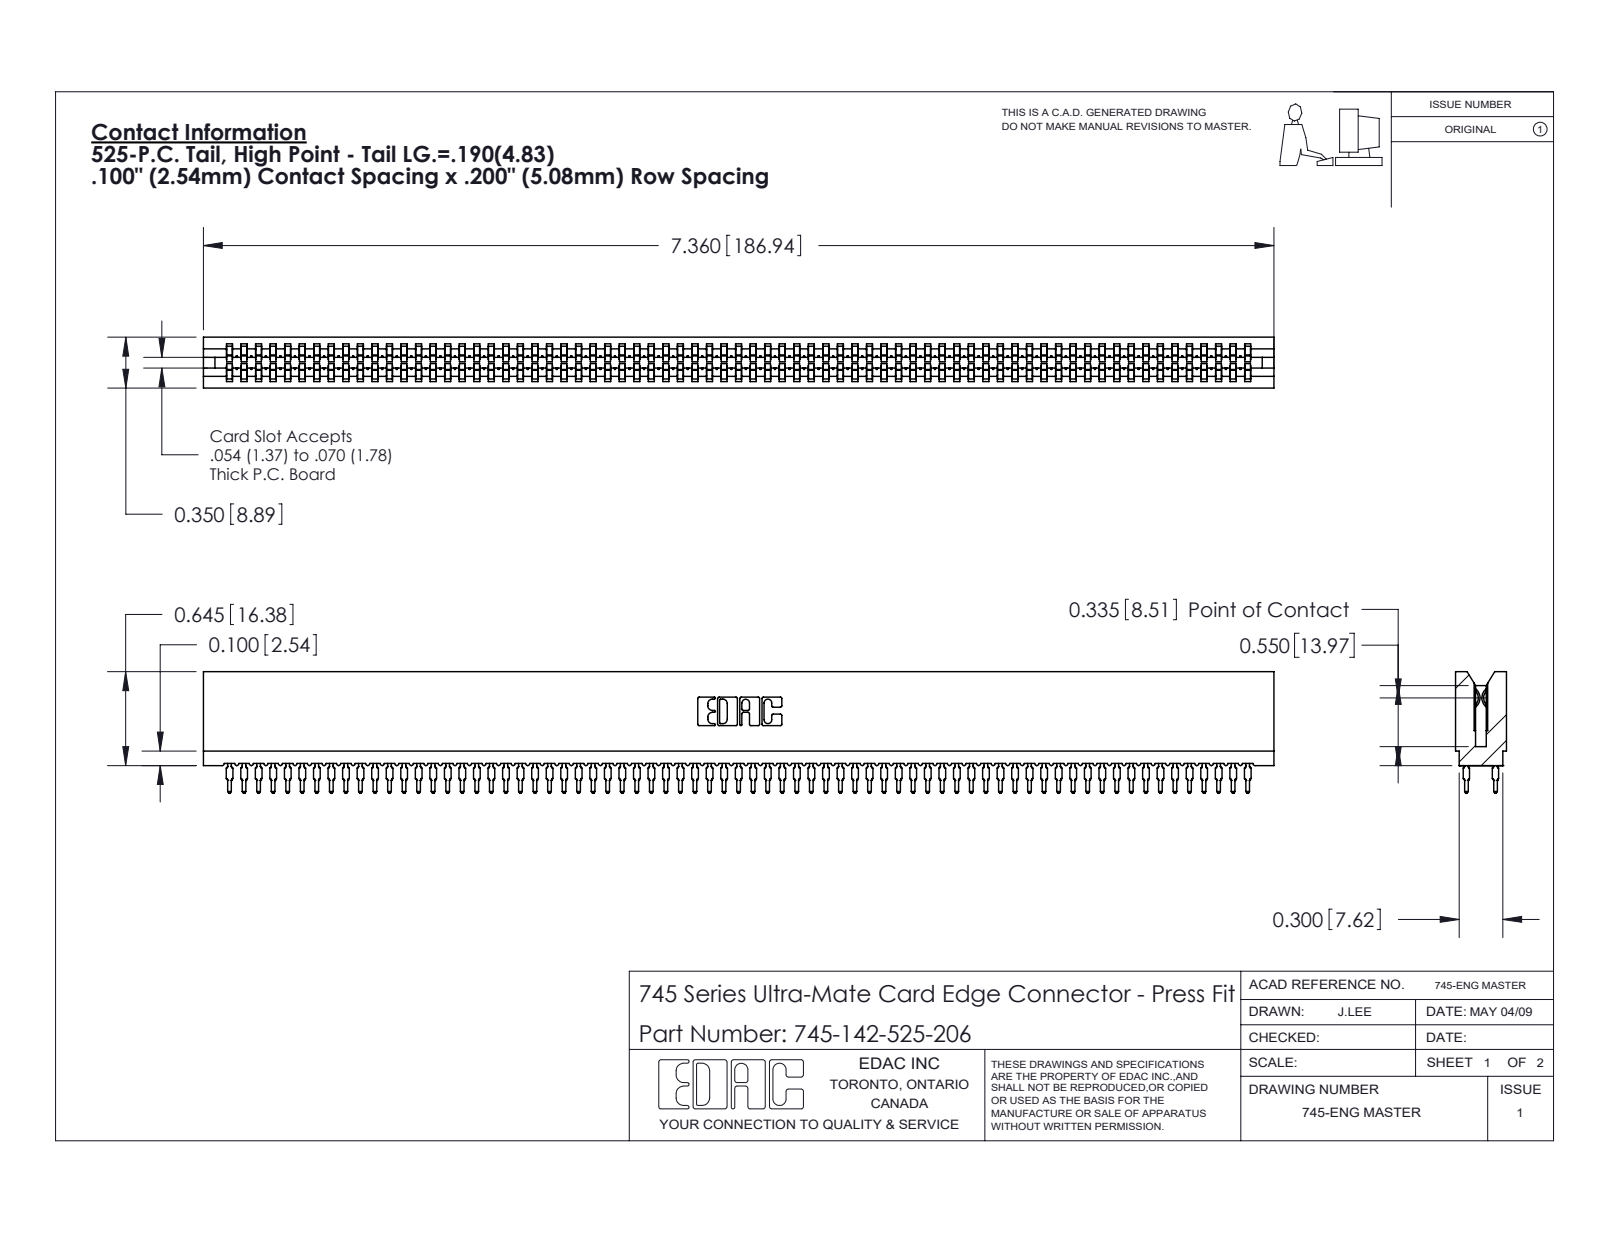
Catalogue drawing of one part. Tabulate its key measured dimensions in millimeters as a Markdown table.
| quantity | value |
| --- | --- |
| part name | 745 Part_Insulator Option - 06; 745-292-001_525; 745-142-525-206 |
| STEP written by | SolidWorks 2020 (CONFIG_CONTROL_DESIGN) |
| units | millimeters |
| bodies | 143 solids, 12805 faces (6588 planar, 2525 cylindrical, 3692 other) |
| overall size | 186.9 × 21.2 × 8.9 |
| volume | 16 600 mm³ |
| surface area | 34 310 mm² |
| partial cylindrical surfaces (radius × count) | 0.5 × 284, 0.4 × 142, 0.3 × 22, 0.1 × 8, 0.3 × 8, 0.2 × 6, 0.8 × 6, 0.7 × 3 |
| main face-to-face distances | 8.9, 1.6, 7.3, 1.1, 7.7, 0.5, 6.2, 3.5, 5.4, 2.4 |
